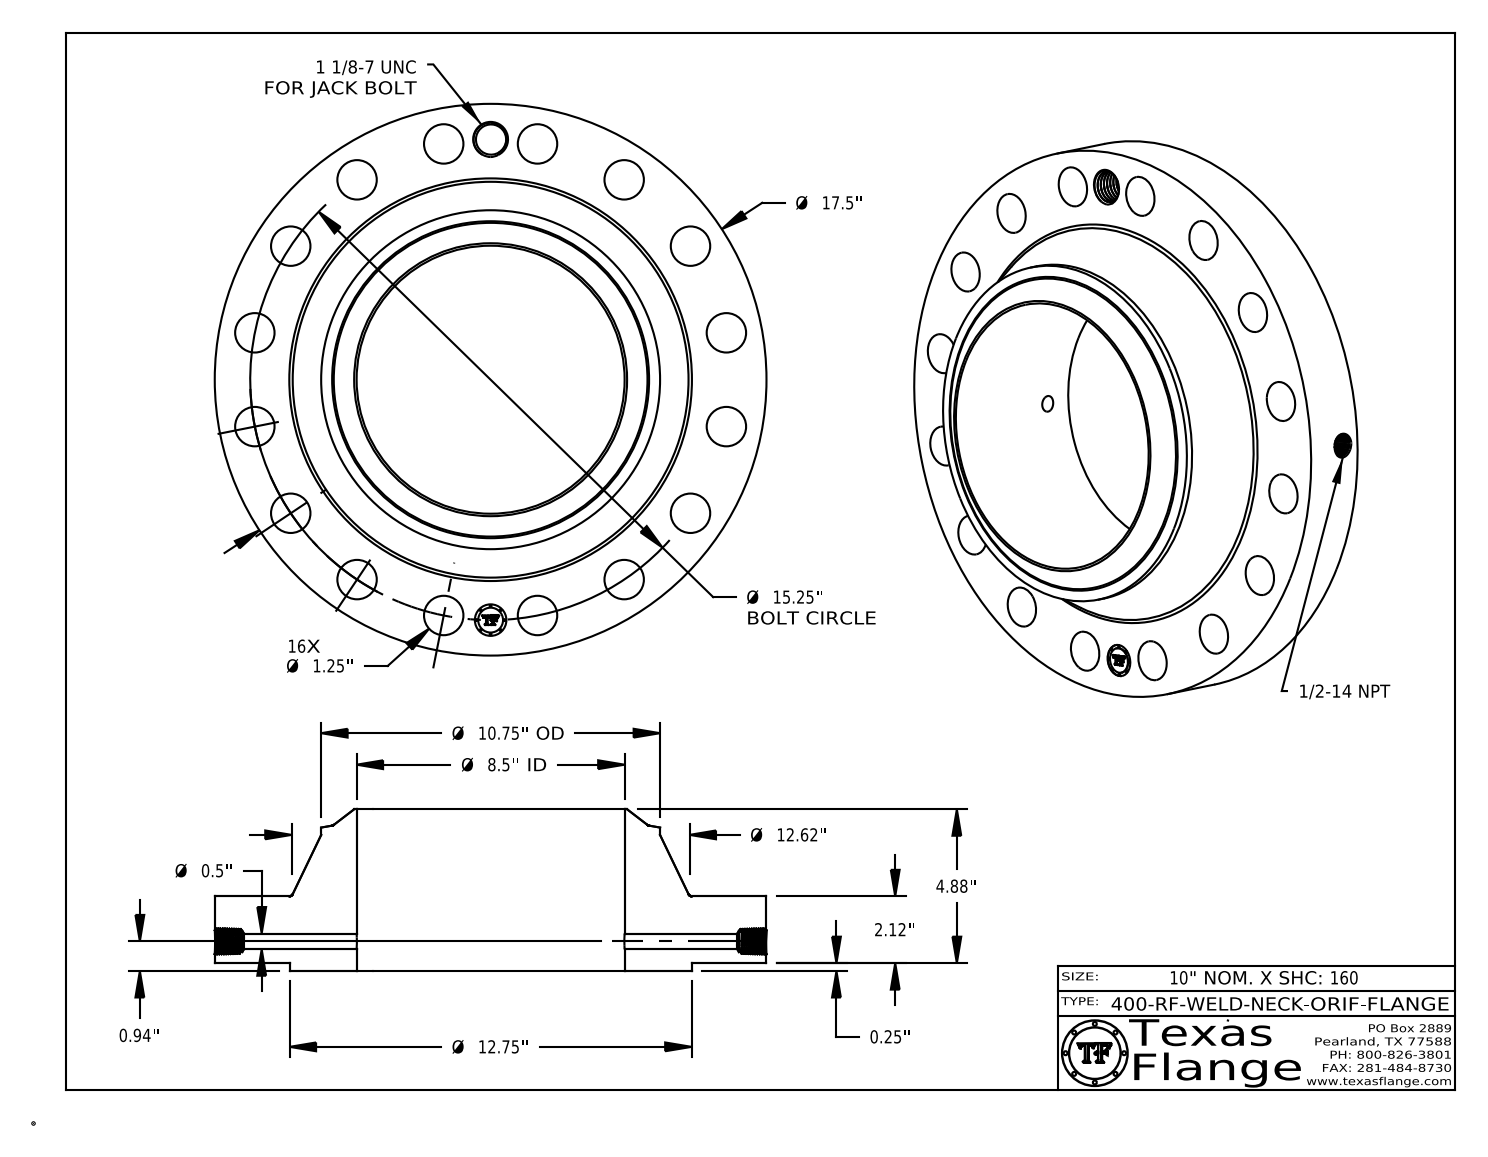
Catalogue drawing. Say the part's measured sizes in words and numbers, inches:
The part is named "400-RF-WELD-NECK". Its 3-D file was written by "CATIA V5 STEP AP214 (AUTOMOTIVE_DESIGN)". It is 1 solid with 789 faces: 369 planar, 109 cylindrical and 311 other. Overall it measures 17.5 by 17.5 by 5.13 inches. Its volume is 476.2 cubic inches and its surface area 808.2 square inches. Round holes: 16 of diameter 1.25, 1 of diameter 0.5, 1 of diameter 0.672, 1 of diameter 0.984, 1 of diameter 1, 1 of diameter 8.5. Round bosses or shafts: 8 of diameter 0.061, 1 of diameter 17.5, 1 of diameter 12.75, 1 of diameter 10.75, 1 of diameter 0.788. The main face-to-face distances are 2.12, 0.25, 2.37, 5.13, 4.88, 2.76, 0.015, 2.355, 2.105, 2.775. The hole center spacings are 5.836, 7.625, 10.783, 14.089, 14.957, 2.975, 2.975, 8.472.
